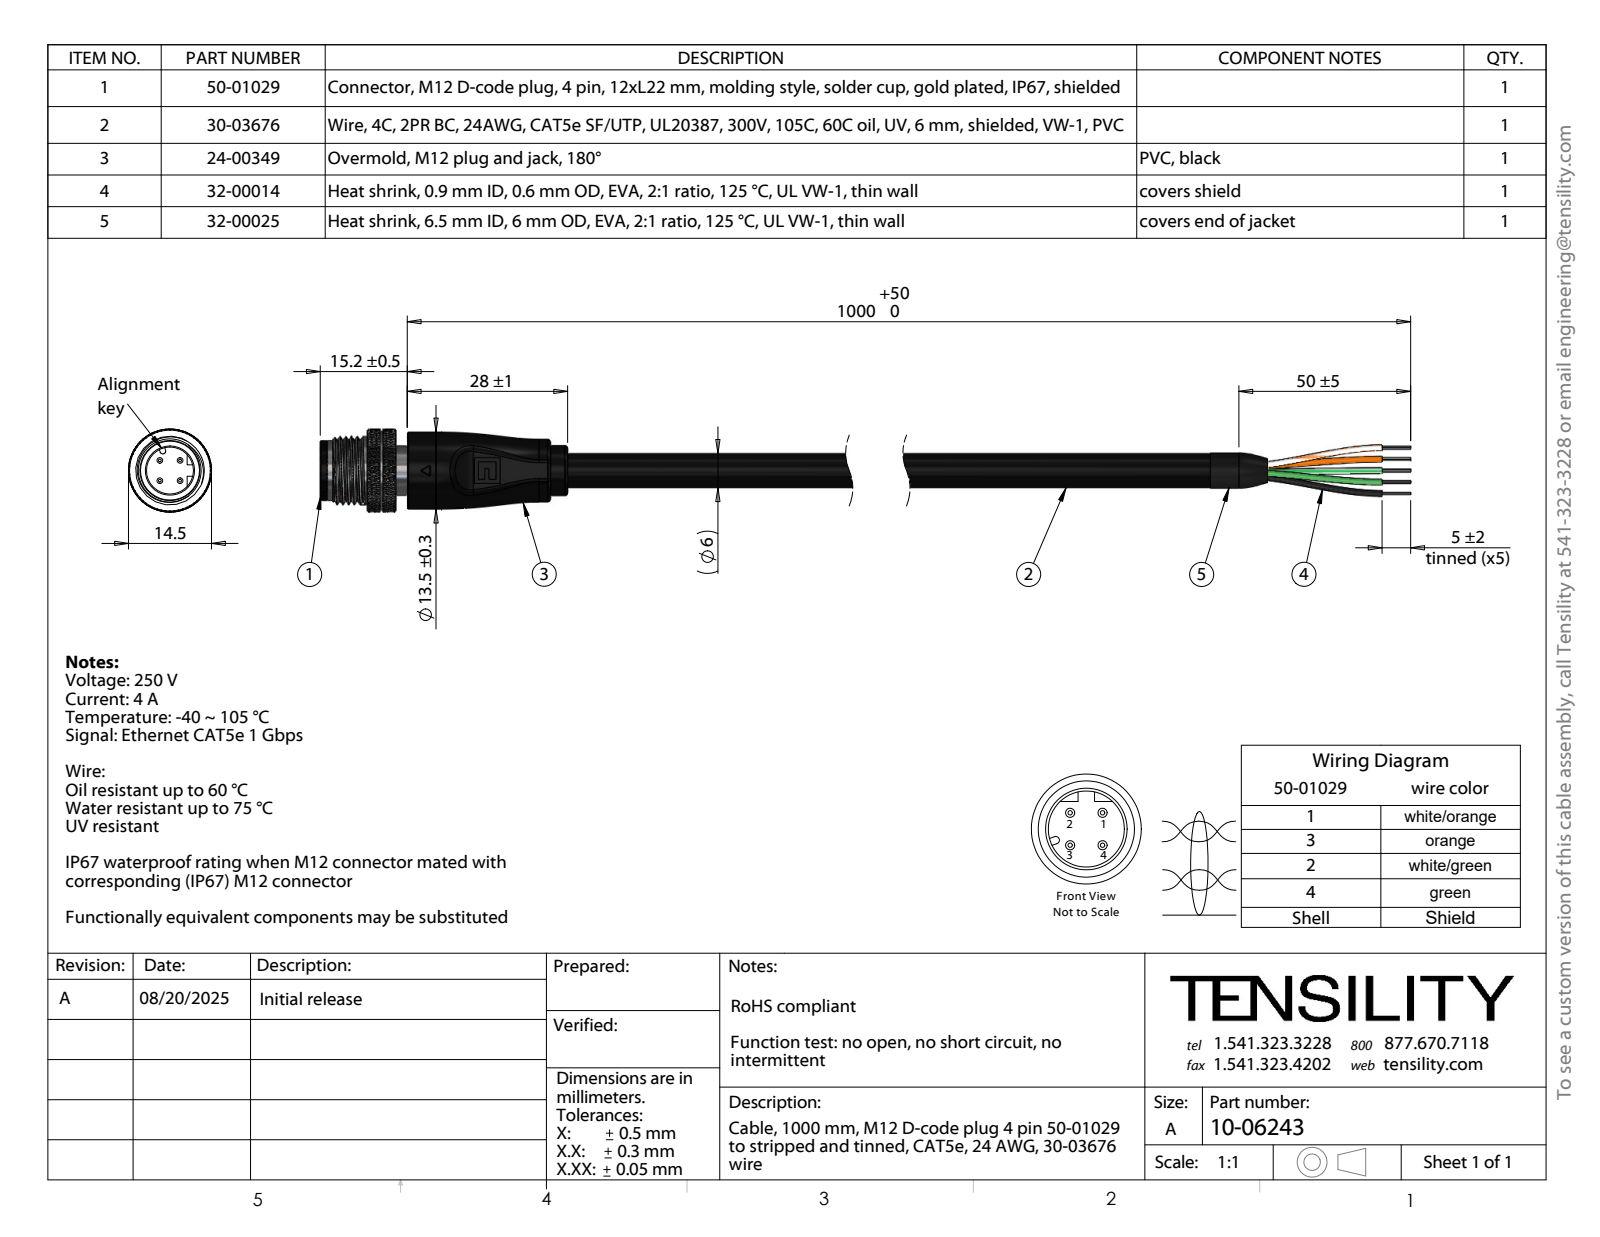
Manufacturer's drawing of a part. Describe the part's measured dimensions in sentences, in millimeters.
The part is named "50-01029-03_默认; 10-06243; 50-01029-01_默认; 30-03676_s + t (+4 more)". Its 3-D file was written by "SolidWorks 2025 (CONFIG_CONTROL_DESIGN)". It is 86 solids with 2792 faces: 263 planar, 823 cylindrical and 1706 other. Overall it measures 223.2 by 14.5 by 14.5 millimeters. Its volume is 9 287 cubic millimeters and its surface area 26 453 square millimeters. Round holes: 28 of diameter 0.2, 4 of diameter 1, 4 of diameter 1.05, 1 of diameter 3.16, 1 of diameter 3.21, 1 of diameter 3.36, 1 of diameter 8, 1 of diameter 8.2, 1 of diameter 8.8, 1 of diameter 9.5. Round bosses or shafts: 35 of diameter 0.2, 4 of diameter 1.4, 1 of diameter 14.5, 1 of diameter 13.9, 1 of diameter 13.5, 1 of diameter 12, 1 of diameter 11, 1 of diameter 10.5. Partial cylindrical surfaces (rounded edges, fillets, slot ends): 2 of radius 0.5, 2 of radius 1.5, 2 of radius 1.96, 1 of radius 5, 1 of radius 5.58, 1 of radius 6.75. The main face-to-face distances are 180, 7, 2, 178, 5, 28, 30, 150, 10.8, 3.8. The hole center spacings are 1.91, 2.09, 1.06, 0.35, 0.89, 1.08, 1.24, 1.71.
